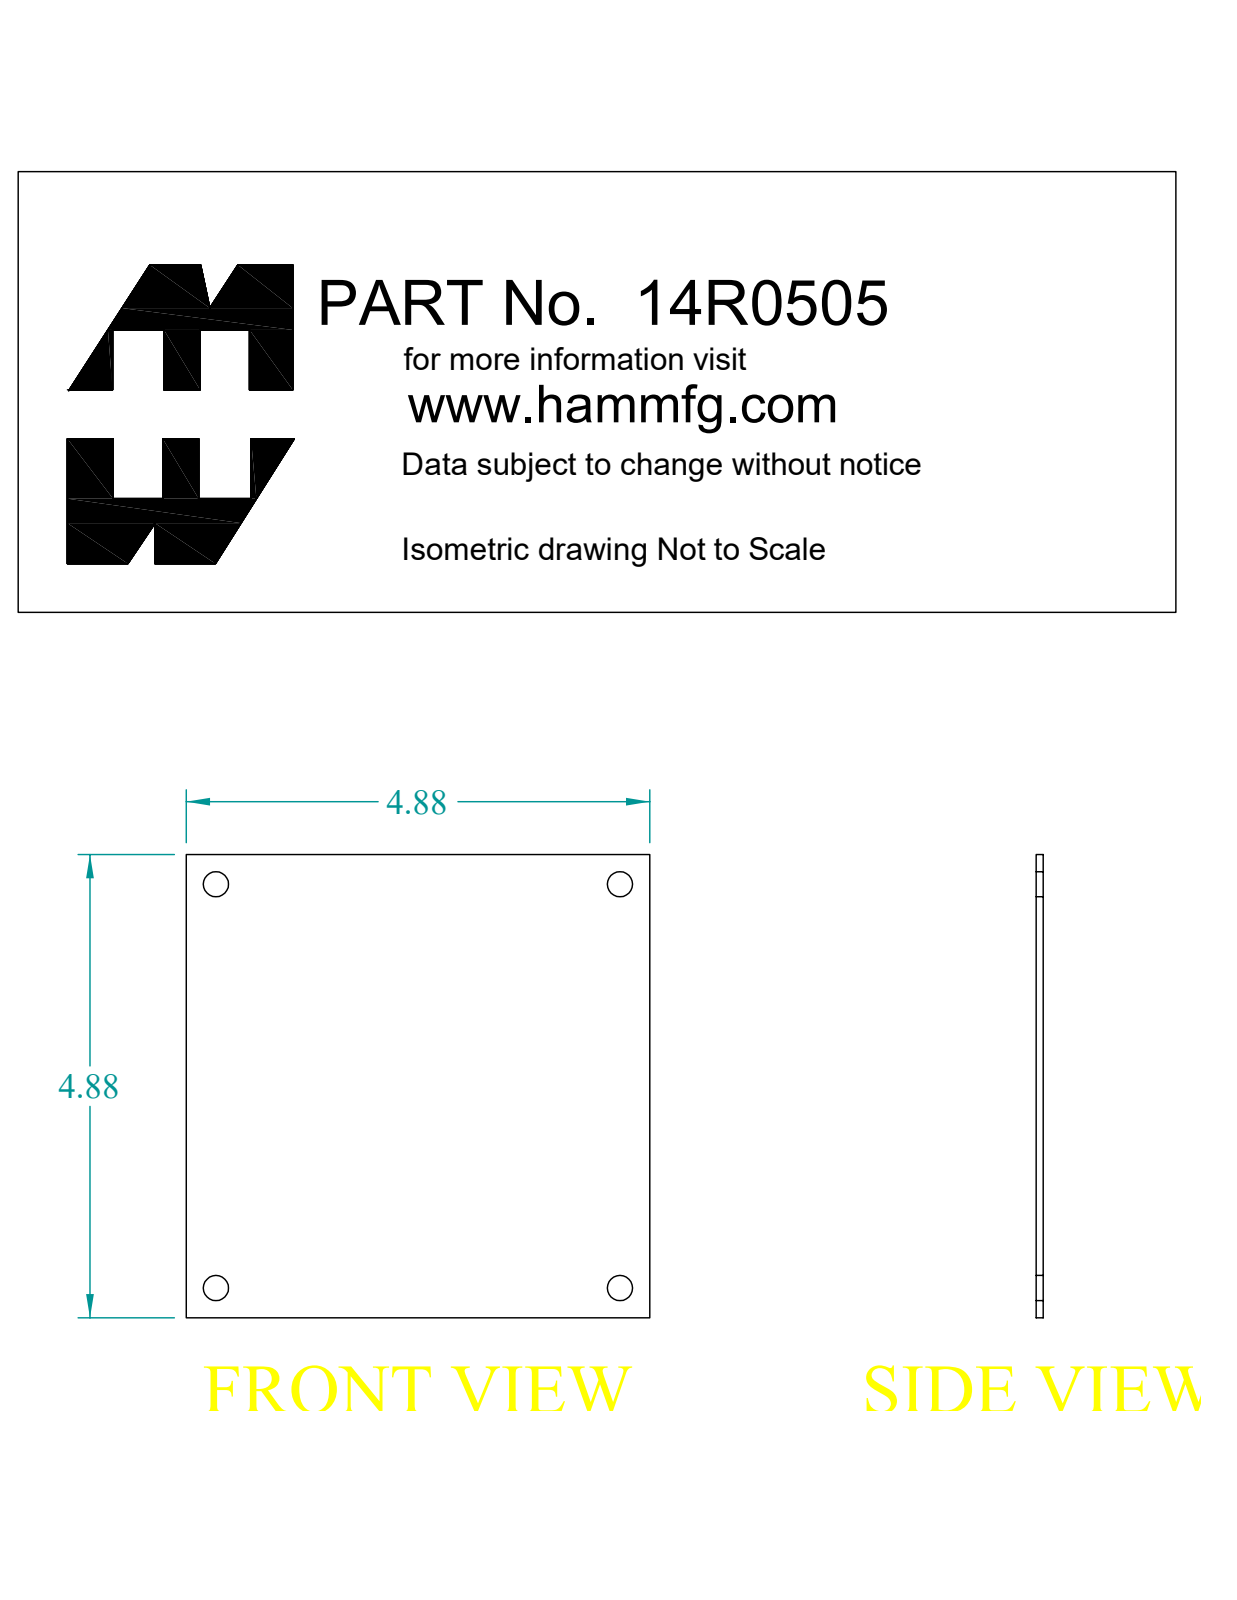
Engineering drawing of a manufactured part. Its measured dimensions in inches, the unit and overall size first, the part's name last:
Units: inches
Overall size (bounding box): 4.875 × 2.875 × 0.072
Round holes (diameter × count): ⌀0.265 ×4
Main face-to-face distances: 0.072, 2.875, 4.875
Hole centre spacings: 2.25, 4.25, 4.808
Volume: 0.993 in³ · Surface area: 28.95 in²
Bodies: 1 solid, 10 faces (6 planar, 4 cylindrical, 0 other)
Part name (STEP PRODUCT): 14R0505
STEP written by: SolidWorks 2018 (AUTOMOTIVE_DESIGN)
